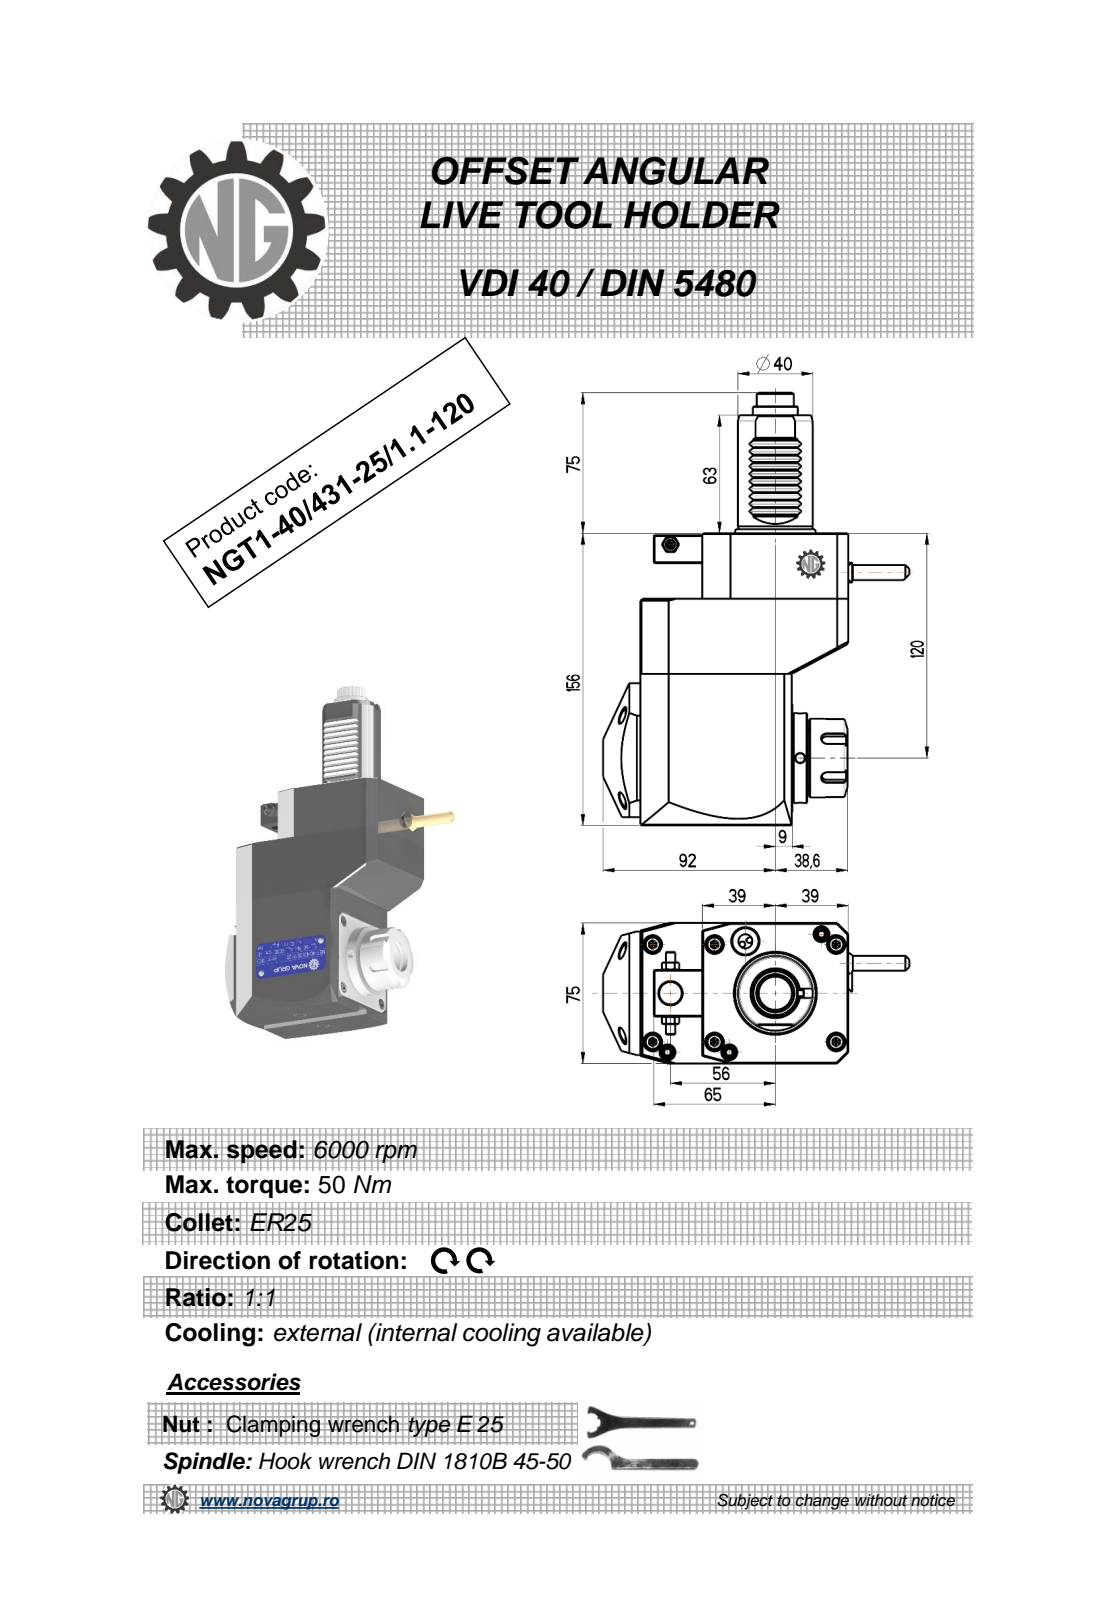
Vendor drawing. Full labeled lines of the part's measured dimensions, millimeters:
Part name (STEP PRODUCT): NGT1_40_431_25_1_1_120
STEP written by: PRO/ENGINEER BY PARAMETRIC TECHNOLOGY CORPORATION, 2010280 (CONFIG_CONTROL_DESIGN)
Units: millimetres
Bodies: 1 solid, 569 faces (212 planar, 185 cylindrical, 172 other)
Overall size (bounding box): 231 × 163.5 × 75
Volume: 1 177 000 mm³ · Surface area: 87 390 mm²
Round holes (diameter × count): ⌀5 ×3, ⌀3 ×1, ⌀4.2 ×1, ⌀9.5 ×1, ⌀12 ×1, ⌀20.3 ×1
Round bosses / shafts (diameter × count): ⌀48 ×1, ⌀42 ×1, ⌀40 ×1, ⌀37.5 ×1, ⌀33 ×1, ⌀24 ×1, ⌀11.2 ×1, ⌀8.96 ×1
Partial cylindrical surfaces — rounded edges, fillets, slot ends (radius × count): R2.08 ×48, R0.26 ×12, R0.3 ×10, R0.22 ×6, R3 ×5, R9.08 ×1, R9.92 ×1, R15 ×1
Main face-to-face distances: 75, 156, 111, 35, 30, 121, 81, 33, 48, 78
Hole centre spacings: 20.3, 69.25, 100.28, 111.5, 133.39
